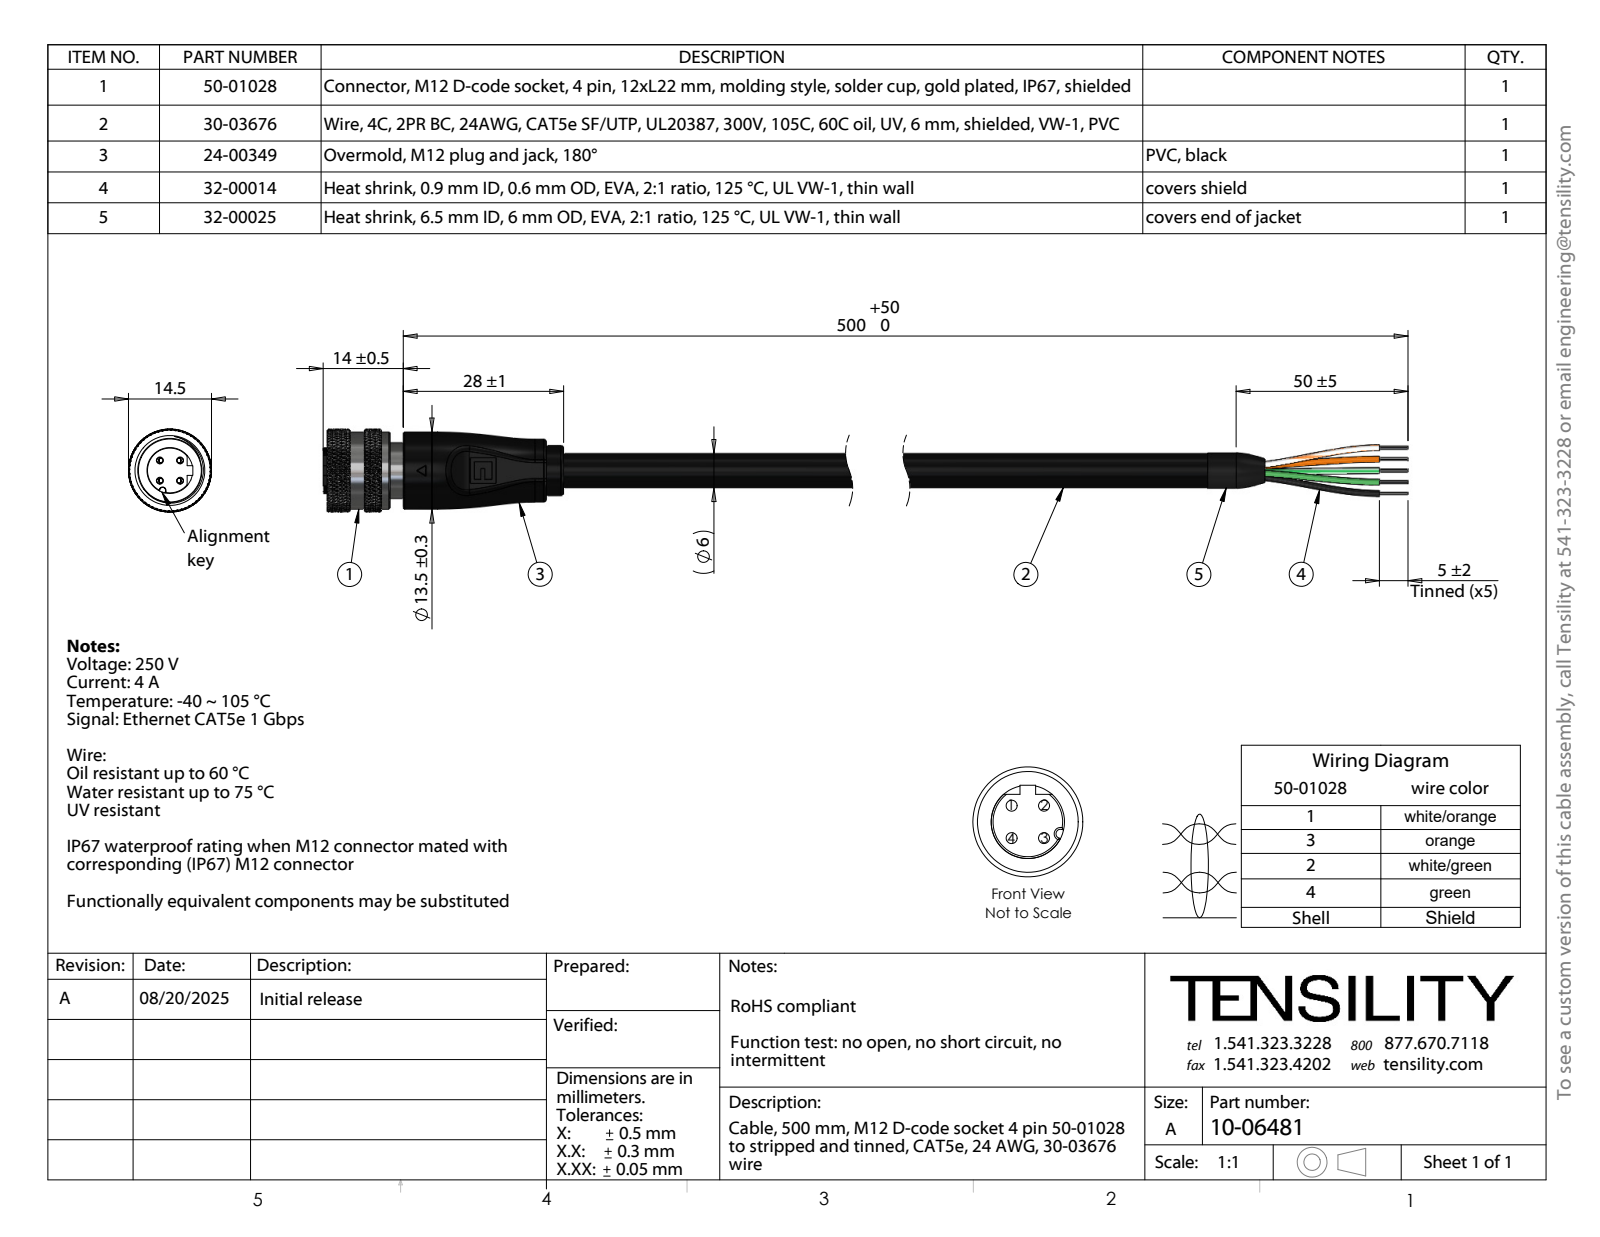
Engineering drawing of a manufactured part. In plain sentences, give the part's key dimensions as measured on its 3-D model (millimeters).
The part is named "50-01028-03_默认; 50-01028_默认; 30-03676_s + t; 24-00349_Mexico (+5 more)". Its 3-D file was written by "SolidWorks 2025 (CONFIG_CONTROL_DESIGN)". It is 87 solids with 3550 faces: 339 planar, 940 cylindrical and 2271 other. Overall it measures 222 by 14.5 by 14.5 millimeters. Its volume is 9 616 cubic millimeters and its surface area 27 027 square millimeters. Round holes: 28 of diameter 0.2, 4 of diameter 1.05, 4 of diameter 1.1, 4 of diameter 1.2, 1 of diameter 3.16, 1 of diameter 3.21, 1 of diameter 3.36, 1 of diameter 9, 1 of diameter 10, 1 of diameter 11.2. Round bosses or shafts: 35 of diameter 0.2, 4 of diameter 1.6, 4 of diameter 1.5, 1 of diameter 13.5, 1 of diameter 11, 1 of diameter 10.6, 1 of diameter 10.5, 1 of diameter 9.8. Partial cylindrical surfaces (rounded edges, fillets, slot ends): 10 of radius 0.1, 6 of radius 0.4, 2 of radius 0.5, 2 of radius 1.5, 1 of radius 4, 1 of radius 5, 1 of radius 5.58, 1 of radius 6.75. The main face-to-face distances are 178, 28, 150, 7, 4.7, 1, 31.8, 3.5, 23.3, 173.3. The hole center spacings are 1.91, 0.36, 2.09, 1.06, 0.89, 1.08, 1.24, 1.8.
